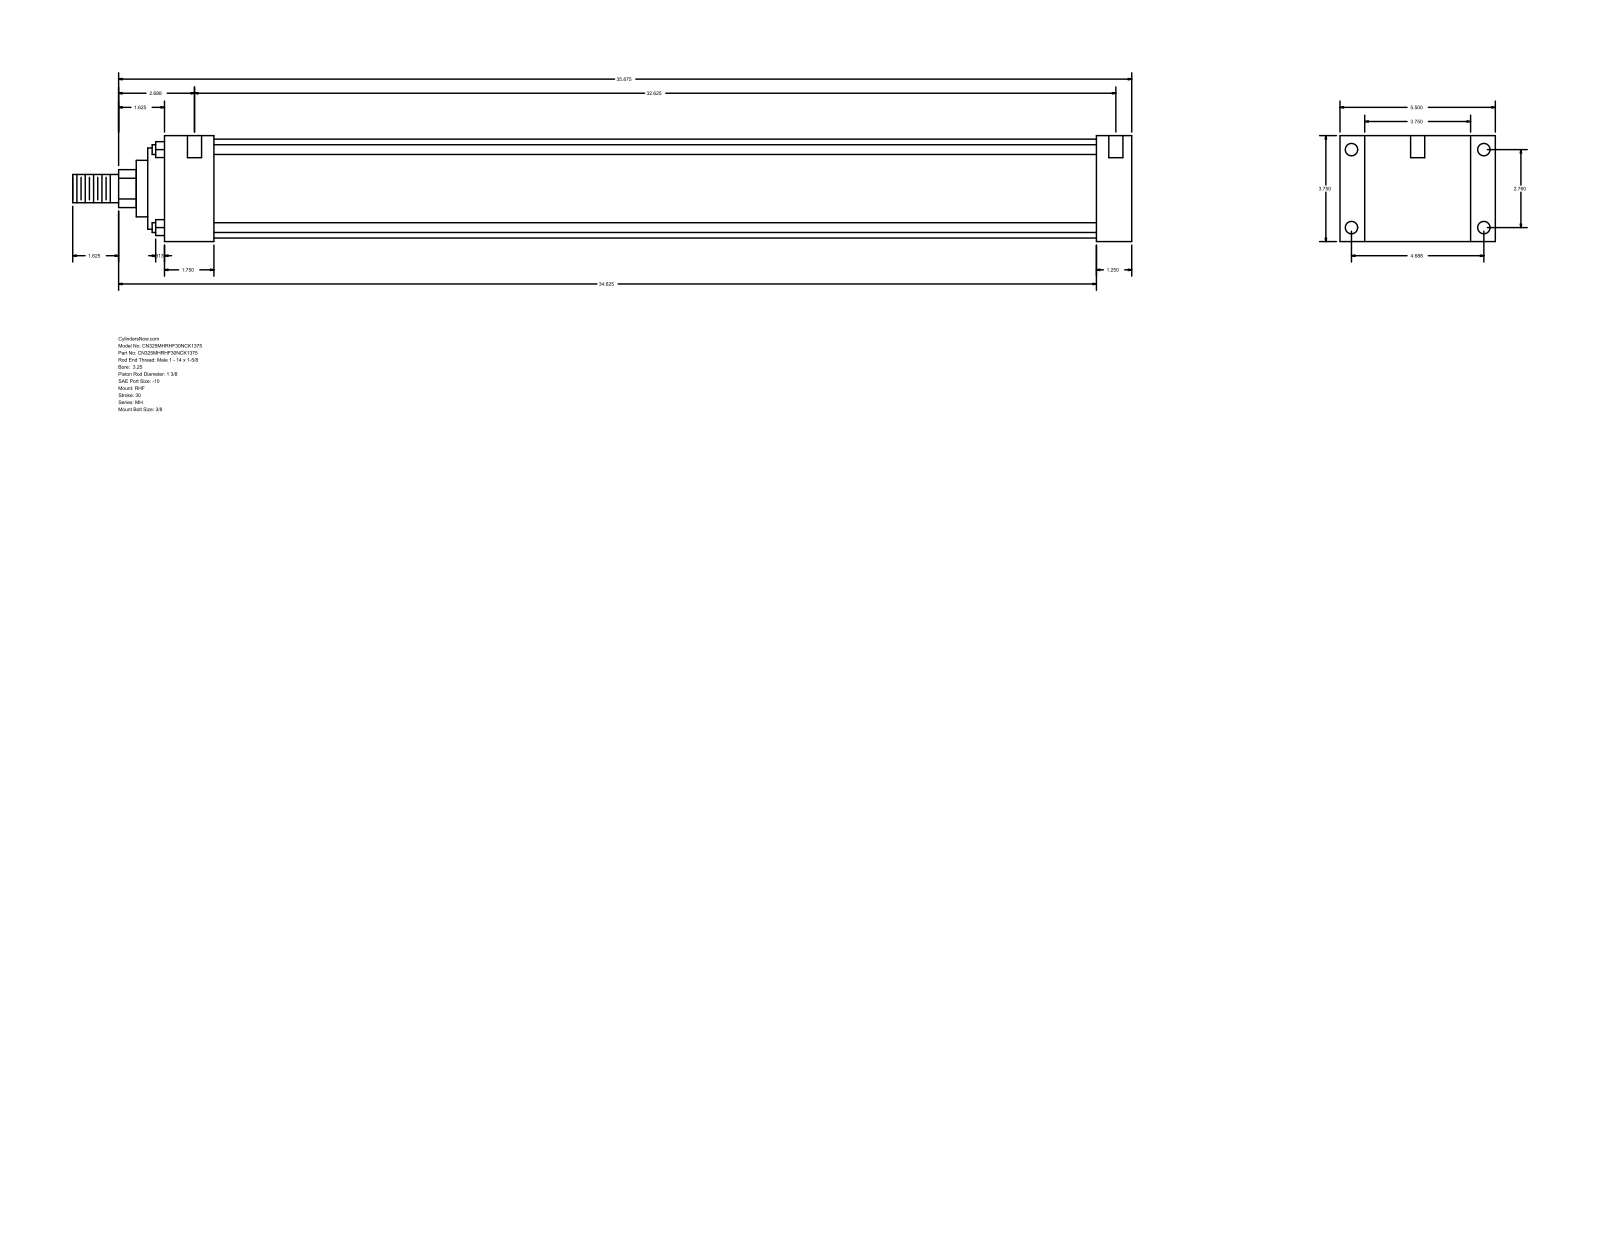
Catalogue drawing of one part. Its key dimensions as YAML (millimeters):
part_name: "MH_RHF__0325_1.375"
step_written_by: "GSSL Pune (CONFIG_CONTROL_DESIGN)"
units: millimeters
bodies: {solids: 0, faces: 90, planar: 61, cylindrical: 29, other: 0}
overall_size: [952.5, 139.7, 95.25]
round_holes:
  - {diameter: 5.56, count: 4}
  - {diameter: 11.13, count: 4}
  - {diameter: 12.7, count: 2}
round_bosses_or_shafts:
  - {diameter: 8.76, count: 4}
  - {diameter: 88.9, count: 1}
  - {diameter: 73.03, count: 1}
  - {diameter: 50.8, count: 1}
  - {diameter: 34.92, count: 1}
  - {diameter: 25.4, count: 1}
partial_cylinders:
  - {radius: 17.06, count: 1}
face_to_face_distances: [95.24, 31.75, 22.23, 117.47, 838.21, 869.96, 139.7, 44.45, 793.76, 825.51]
hole_center_spacings: [70.1, 119.06, 138.16, 835.03, 1.59, 4.76, 828.68, 830.27]
